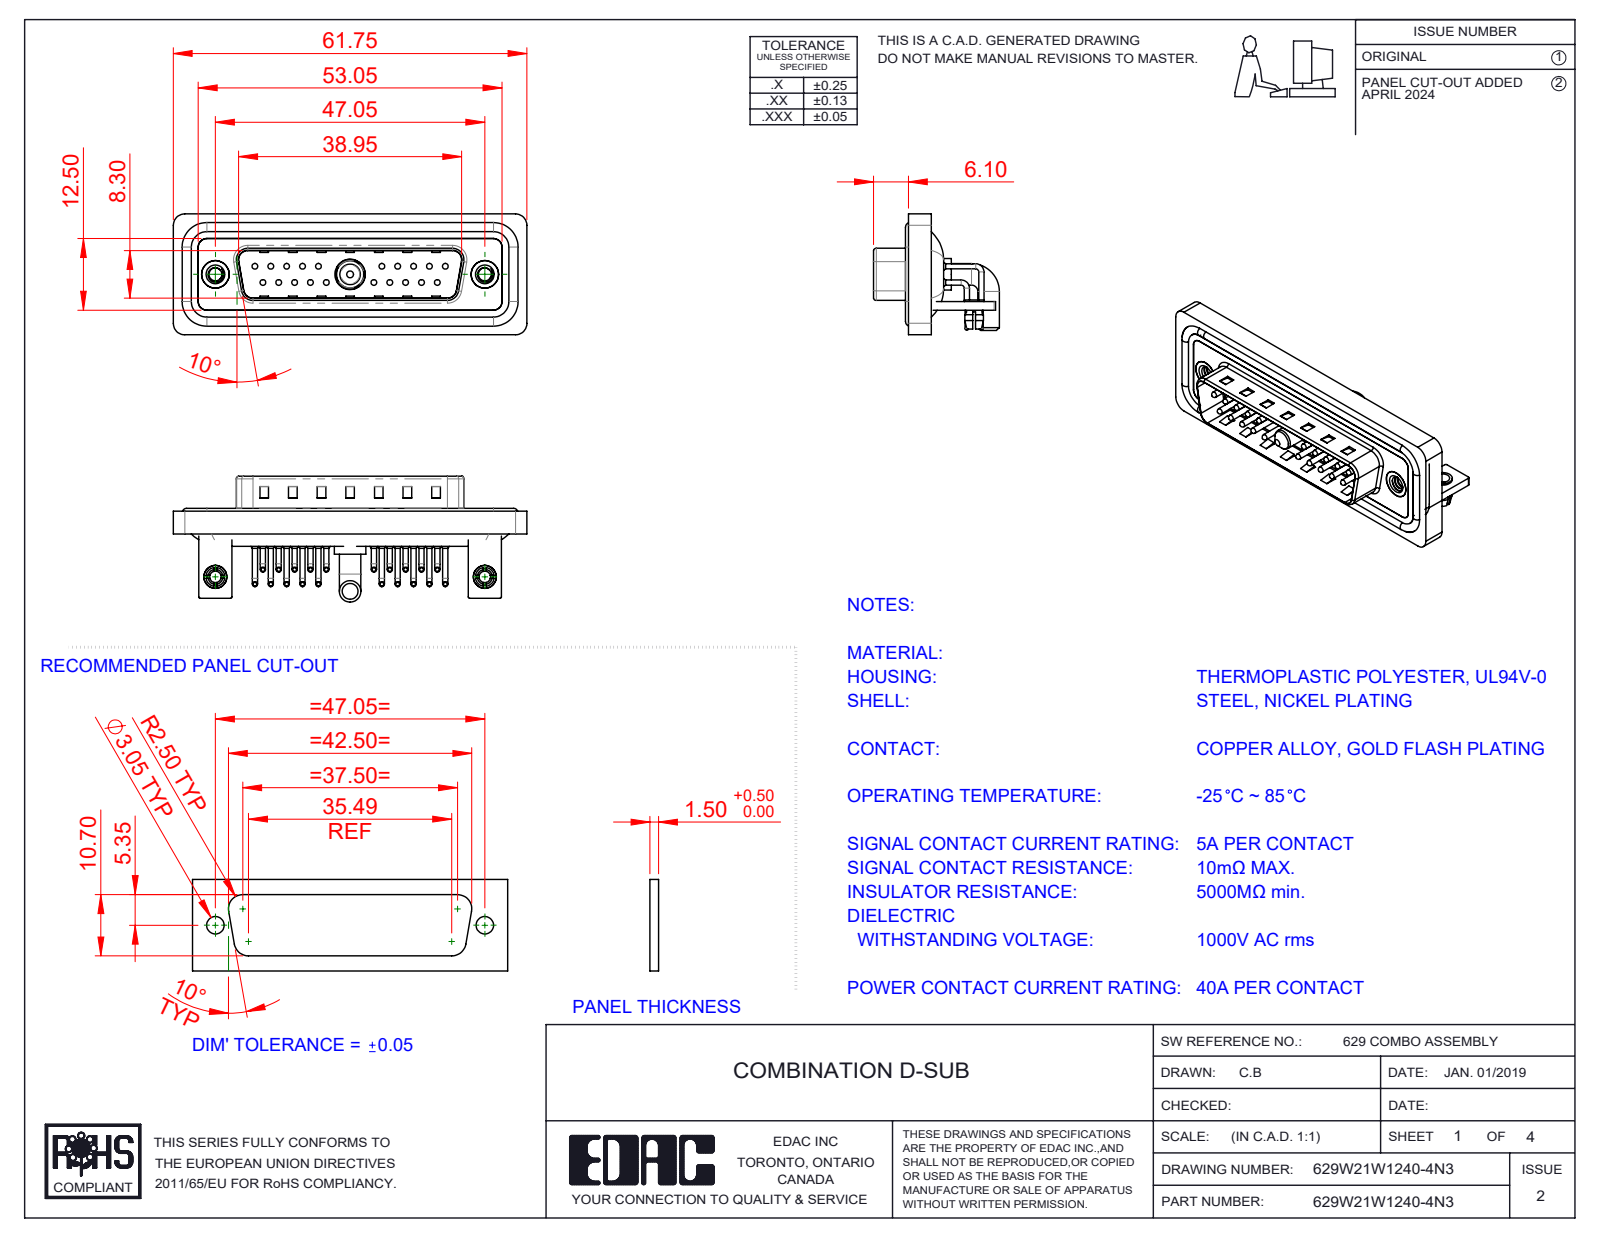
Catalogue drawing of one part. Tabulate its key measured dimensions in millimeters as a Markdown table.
| quantity | value |
| --- | --- |
| part name | 629Combo Contact Row 1; 629Combo Threaded Rivet_3; Power Pin_40A RA; 629Combo Board Lock (+7 more) |
| STEP written by | SolidWorks 2023 (CONFIG_CONTROL_DESIGN) |
| units | millimeters |
| bodies | 33 solids, 2858 faces (1567 planar, 979 cylindrical, 312 other) |
| overall size | 61.75 × 21.98 × 21.1 |
| volume | 7 805 mm³ |
| surface area | 13 562 mm² |
| round holes (diameter × count) | 2 × 22, 0.75 × 20, 1.6 × 20, 2.26 × 2, 2.5 × 2, 3.2 × 2, 4 × 2, 4.8 × 2, 5 × 2, 4.85 × 1, 5.3 × 1 |
| round bosses / shafts (diameter × count) | 0.9 × 40, 1.5 × 20, 1 × 20, 0.65 × 20, 1.6 × 4, 4.9 × 2, 4 × 2, 3.75 × 2 |
| partial cylindrical surfaces (radius × count) | 1.01 × 20, 2 × 19, 1.5 × 18, 0.25 × 16, 0.5 × 9, 1.6 × 8, 0.6 × 4, 0.65 × 4 |
| main face-to-face distances | 0.4, 0.8, 2.1, 2.9, 1.5, 1.1, 4.1, 1.6, 4.5, 3.7 |
| hole center spacings | 3.16, 2.77, 5.54, 8.31, 5.04, 19.39, 20.97, 22.16 |
